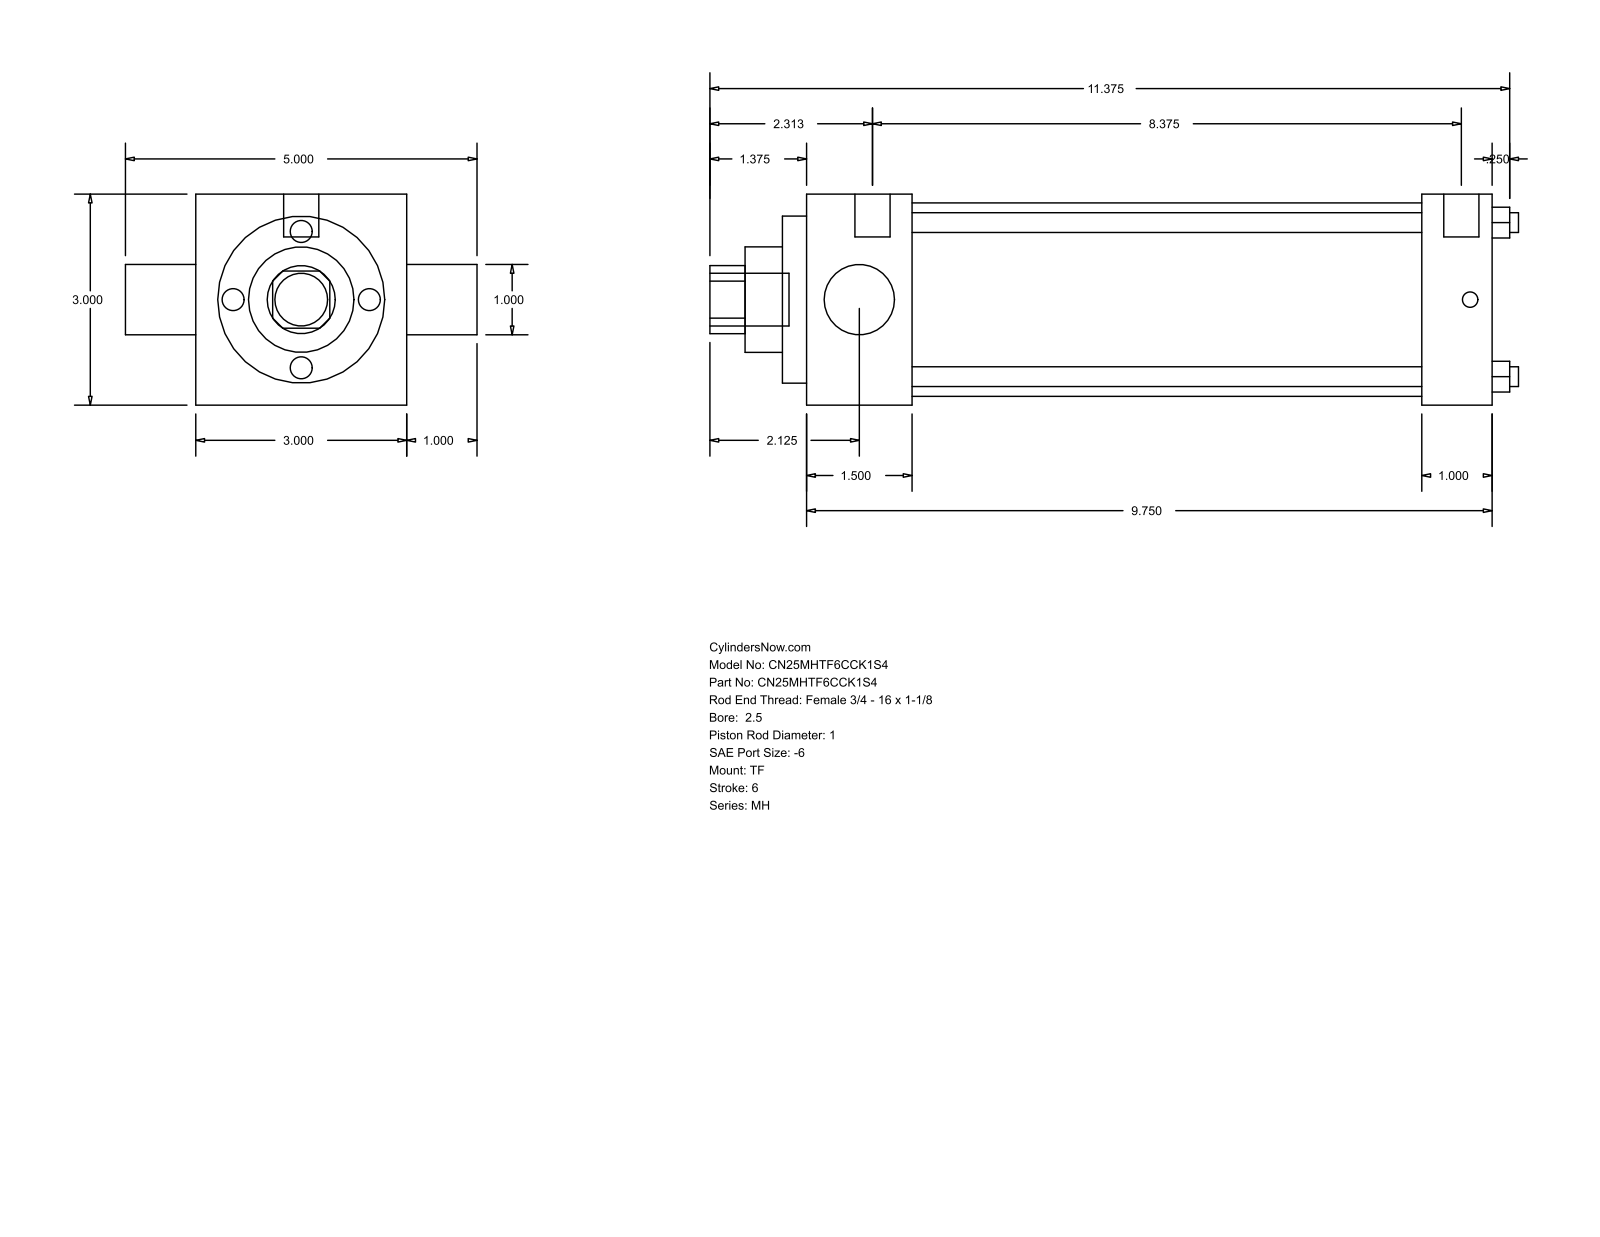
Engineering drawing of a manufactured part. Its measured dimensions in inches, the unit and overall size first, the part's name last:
Units: inches
Overall size (bounding box): 11.5 × 5 × 3
Round holes (diameter × count): ⌀0.281 ×4, ⌀1 ×2, ⌀1.5 ×1, ⌀2.375 ×1, ⌀2.75 ×1
Round bosses / shafts (diameter × count): ⌀0.219 ×3, ⌀0.5 ×2, ⌀0.75 ×1
Partial cylindrical surfaces — rounded edges, fillets, slot ends (radius × count): R0.484 ×1
Main face-to-face distances: 3, 9.75, 1, 1.5, 8.25, 8.75, 7.25, 0.344, 1.844, 9.094
Hole centre spacings: 1.548, 2.19, 3.097
Bodies: 0 solids, 86 faces (61 planar, 25 cylindrical, 0 other)
Part name (STEP PRODUCT): MH_TF__0250_1
STEP written by: GSSL Pune (CONFIG_CONTROL_DESIGN)
